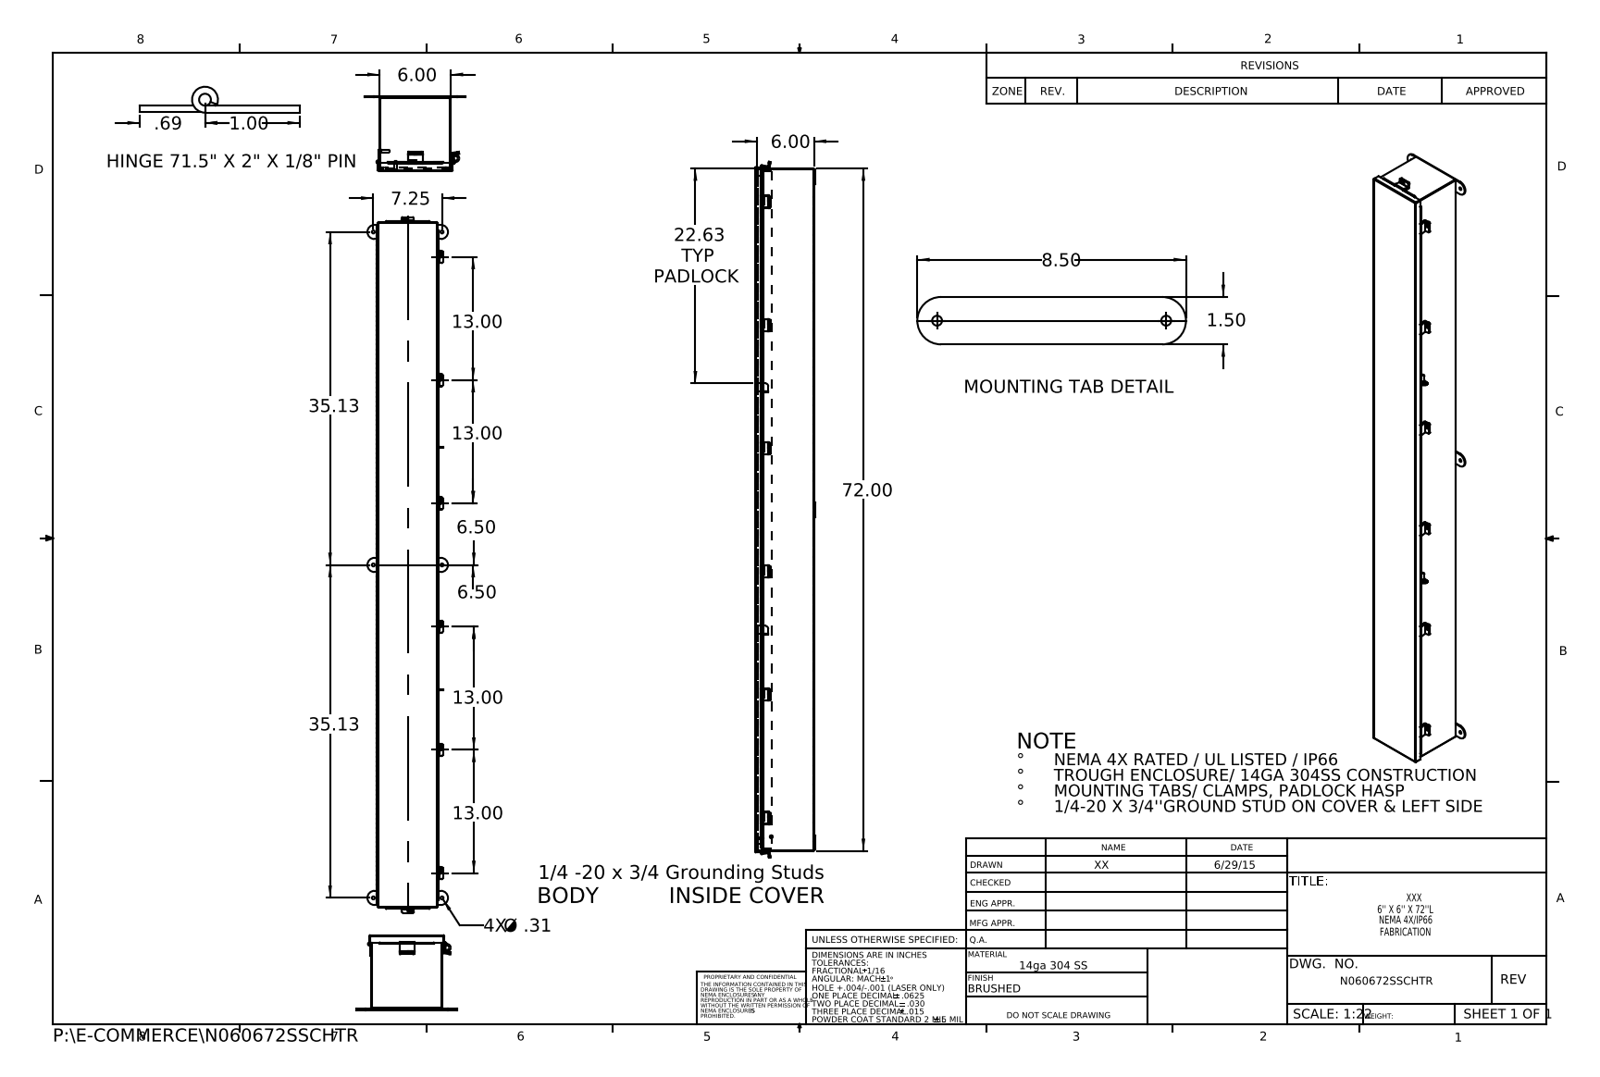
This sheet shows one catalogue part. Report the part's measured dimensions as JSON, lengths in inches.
{"part_name": "N060672SSCHTR JIC Enclosure Template; N060672SSCHTR _JIC Hinge; N060672SSCHTR JIC Clamp Bracket; N060672SSCHTR JIC Mounting (+8 more)", "step_written_by": "SolidWorks 2015 (CONFIG_CONTROL_DESIGN)", "units": "inches", "bodies": {"solids": 29, "faces": 1919, "planar": 1138, "cylindrical": 761, "other": 20}, "overall_size": [73.407, 8.5, 6.337], "volume_in3": 163.1, "surface_area_in2": 4402, "round_holes": [[0.25, 8], [0.313, 6], [0.125, 1], [0.375, 1]], "round_bosses_or_shafts": [[0.315, 2], [0.236, 2], [0.273, 1], [0.25, 1]], "partial_cylinders_radius": [[0.125, 31], [0.133, 16], [0.009, 12], [0.013, 12], [0.088, 12], [0.083, 6], [0.1, 6], [0.75, 6]], "face_to_face_distances": [0.075, 5.925, 6.128, 6, 5.85, 6.203, 6.053, 0.149, 6.074, 0.074], "hole_center_spacings": [13, 26, 35.125, 7.25, 39, 35.865, 35.866, 52]}
